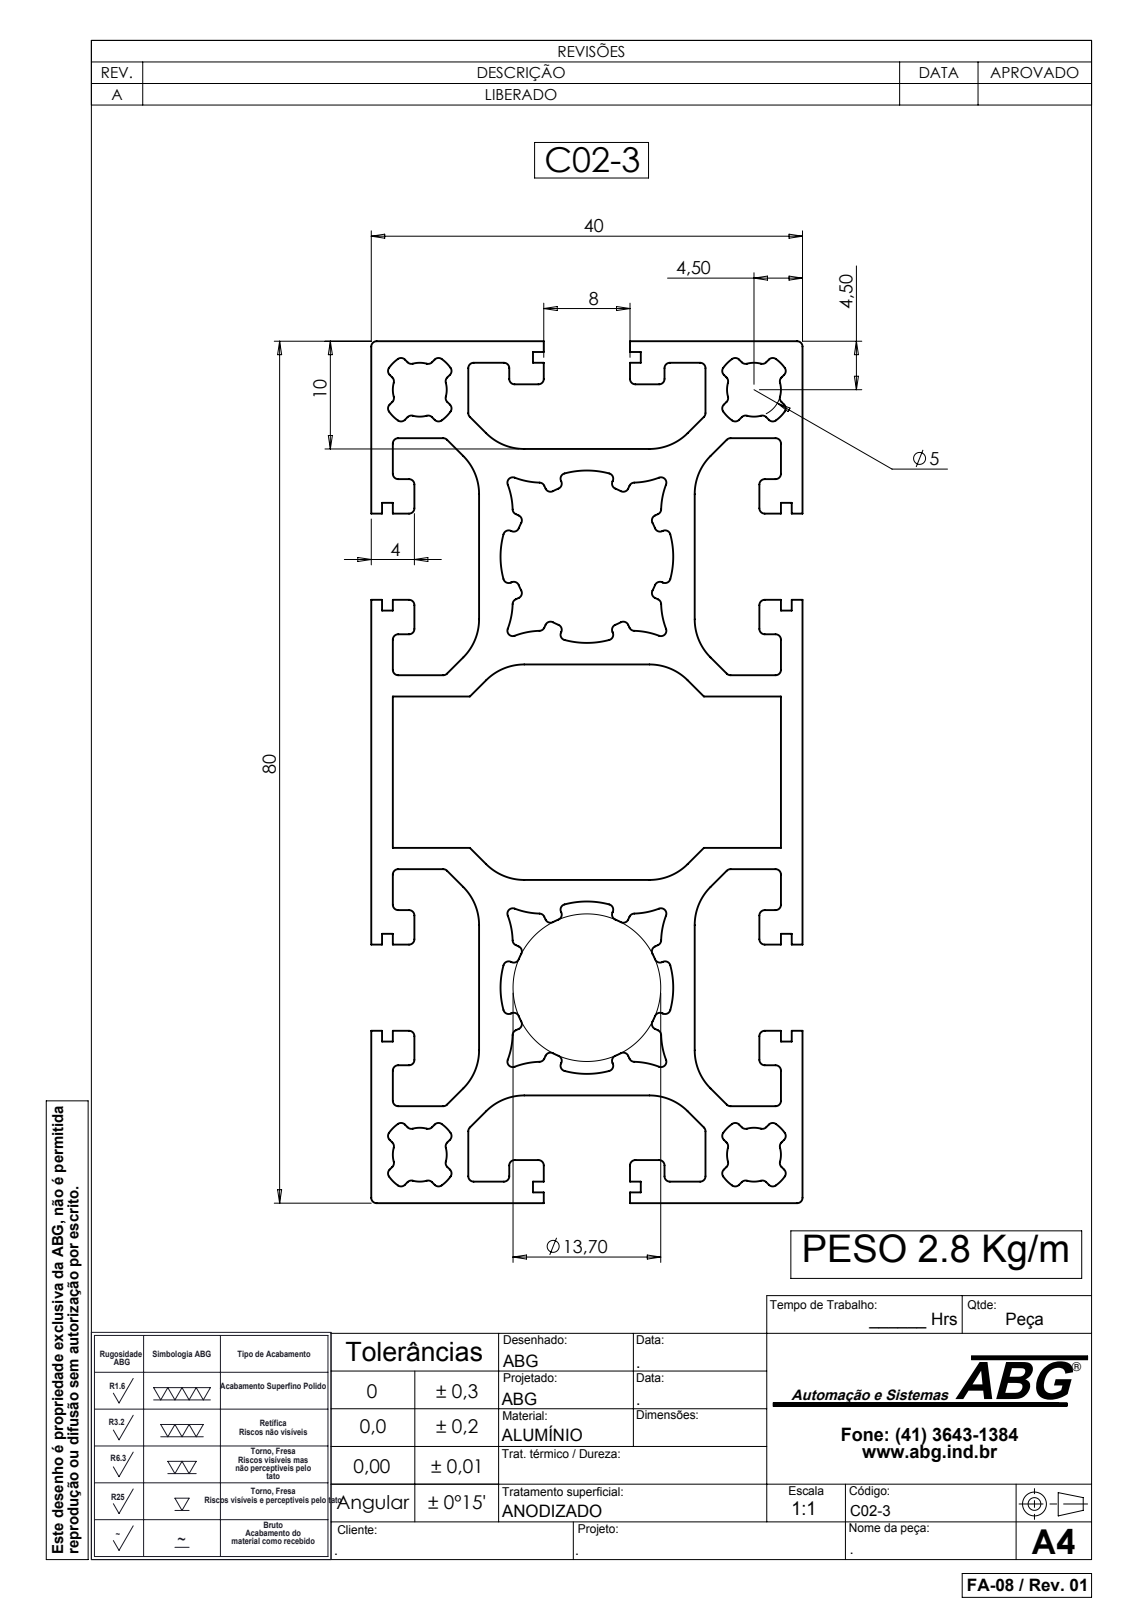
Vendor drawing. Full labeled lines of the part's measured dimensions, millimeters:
Part name (STEP PRODUCT): C02-3
STEP written by: SolidWorks 2007 (CONFIG_CONTROL_DESIGN)
Units: millimetres
Bodies: 1 solid, 540 faces (214 planar, 326 cylindrical, 0 other)
Overall size (bounding box): 6000 × 80 × 40
Volume: 6 261 000 mm³ · Surface area: 5 416 000 mm²
Partial cylindrical surfaces — rounded edges, fillets, slot ends (radius × count): R0.5 ×200, R5 ×16, R7 ×16, R2.5 ×4, R3.5 ×4, R6.85 ×2, R8 ×2, R8.01 ×2
Main face-to-face distances: 40, 2, 8, 30, 20, 10, 1, 38, 7, 28
